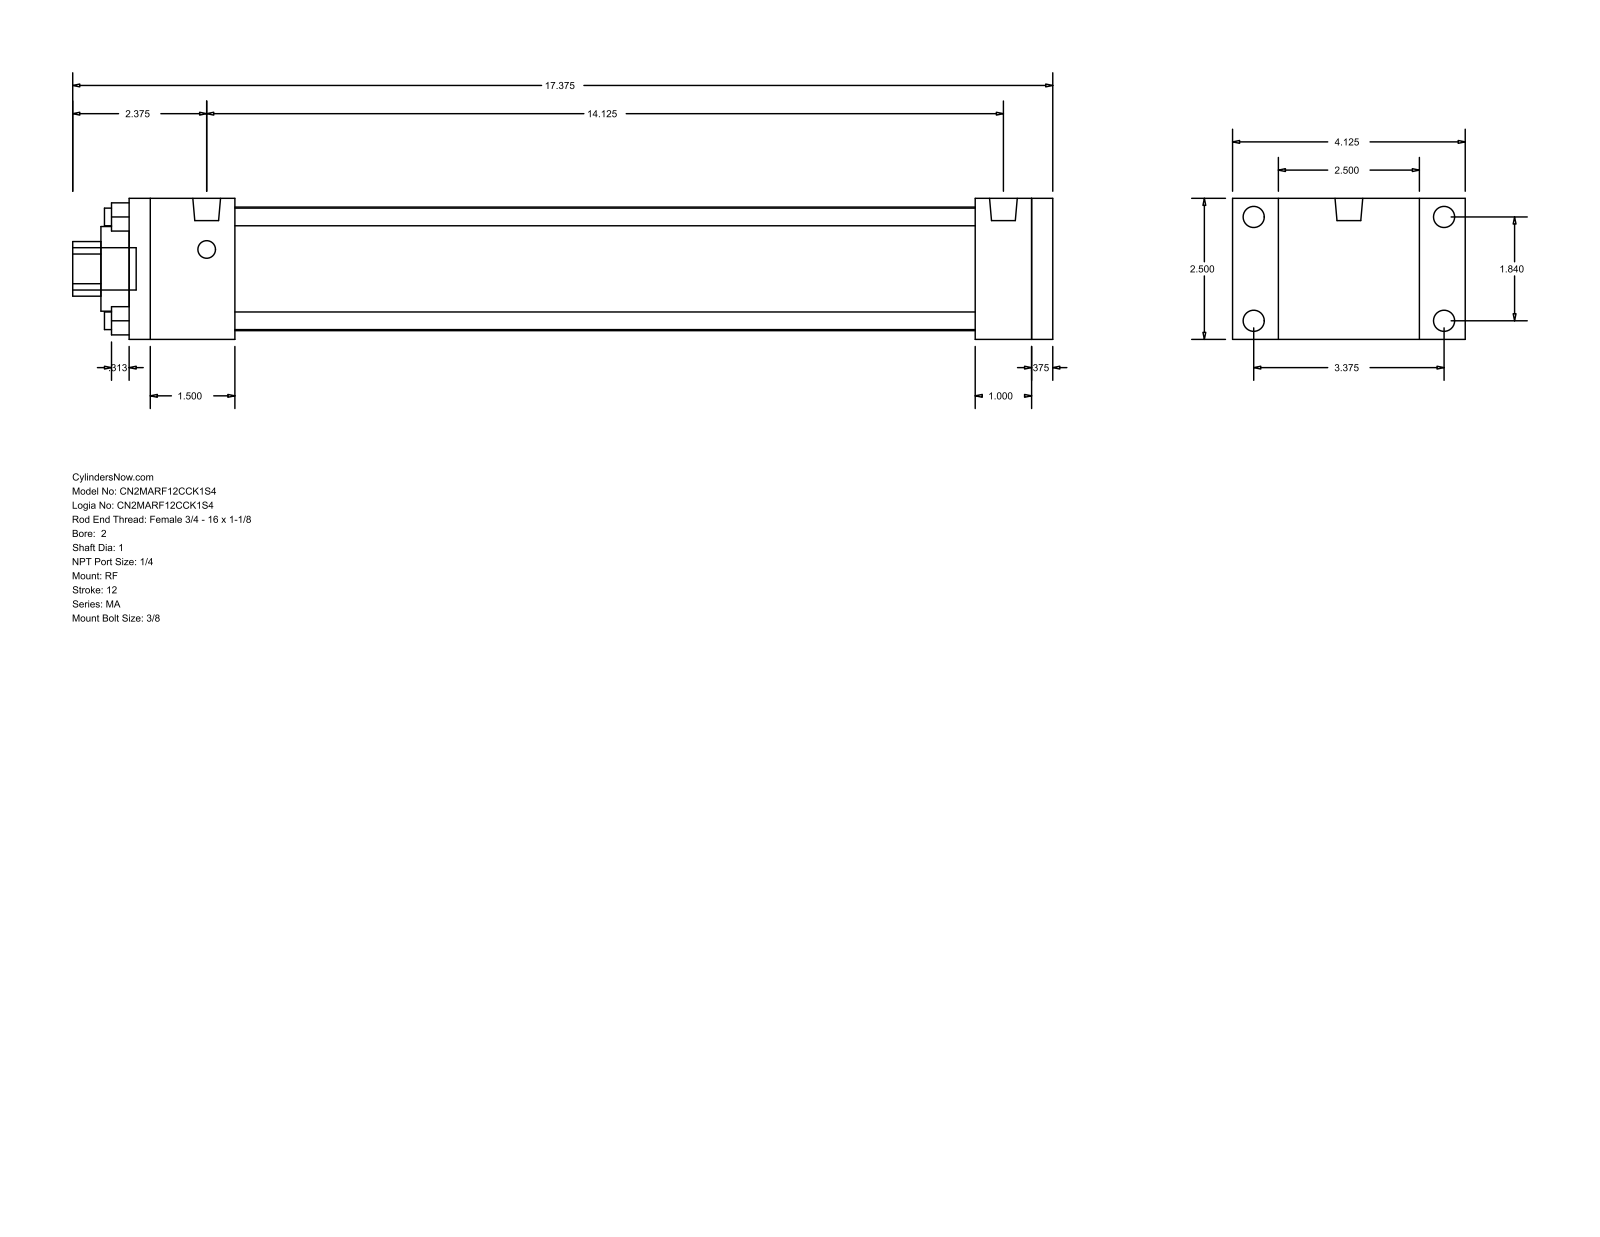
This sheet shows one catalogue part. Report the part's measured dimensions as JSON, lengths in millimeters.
{"part_name": "MA_RF__0200_1", "step_written_by": "GSSL Pune (CONFIG_CONTROL_DESIGN)", "units": "millimeters", "bodies": {"solids": 0, "faces": 92, "planar": 64, "cylindrical": 28, "other": 0}, "overall_size": [441.32, 104.78, 63.5], "round_holes": [[7.94, 4], [25.4, 1], [38.1, 1], [55.63, 1]], "round_bosses_or_shafts": [[9.53, 4], [7.94, 4], [12.49, 2], [19.05, 1]], "partial_cylinders_radius": [[12.29, 1]], "face_to_face_distances": [63.5, 406.4, 9.52, 415.92, 25.4, 20.64, 12.7, 47.63, 358.77, 368.29], "hole_center_spacings": [33.05, 46.74, 66.1]}
